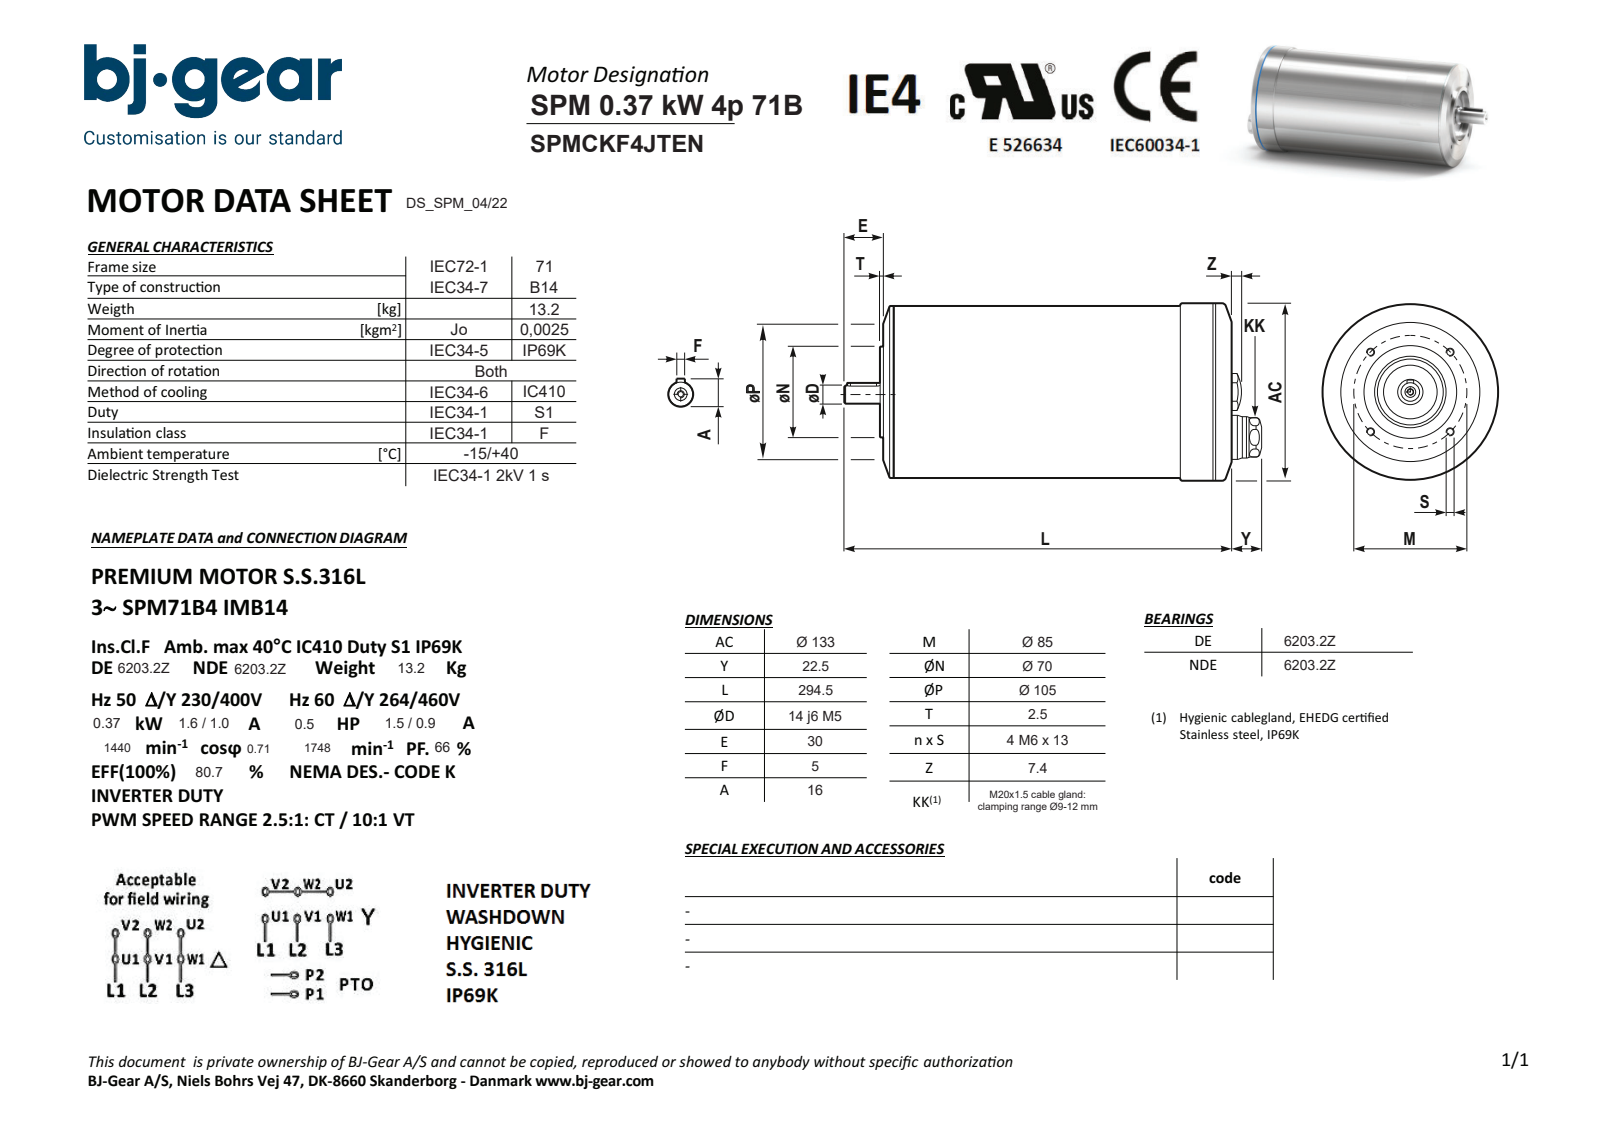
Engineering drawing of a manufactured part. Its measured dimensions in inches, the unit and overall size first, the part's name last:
Units: inches
Overall size (bounding box): 12.677 × 5.236 × 5.236
Round holes (diameter × count): ⌀0.194 ×4, ⌀0.163 ×1, ⌀0.209 ×1, ⌀0.276 ×1, ⌀0.528 ×1, ⌀2.047 ×1, ⌀2.441 ×1
Round bosses / shafts (diameter × count): ⌀5.236 ×1, ⌀5.235 ×1, ⌀5.079 ×1, ⌀5.078 ×1, ⌀2.756 ×1, ⌀0.787 ×1, ⌀0.669 ×1, ⌀0.551 ×1
Partial cylindrical surfaces — rounded edges, fillets, slot ends (radius × count): R0.098 ×2, R0.504 ×1
Main face-to-face distances: 10.413, 10.197, 0.217, 10.374, 0.177, 0.039, 0.098, 0.315, 10.512, 0.138
Hole centre spacings: 1.673, 2.366, 1.193, 2.785, 3.346, 1.339
Volume: 211.8 in³ · Surface area: 214.3 in²
Bodies: 1 solid, 90 faces (31 planar, 33 cylindrical, 26 other)
Part name (STEP PRODUCT): SPMCKF4JTENN4KSA1-N---NNN
STEP written by: Solid Edge (AUTOMOTIVE_DESIGN)
